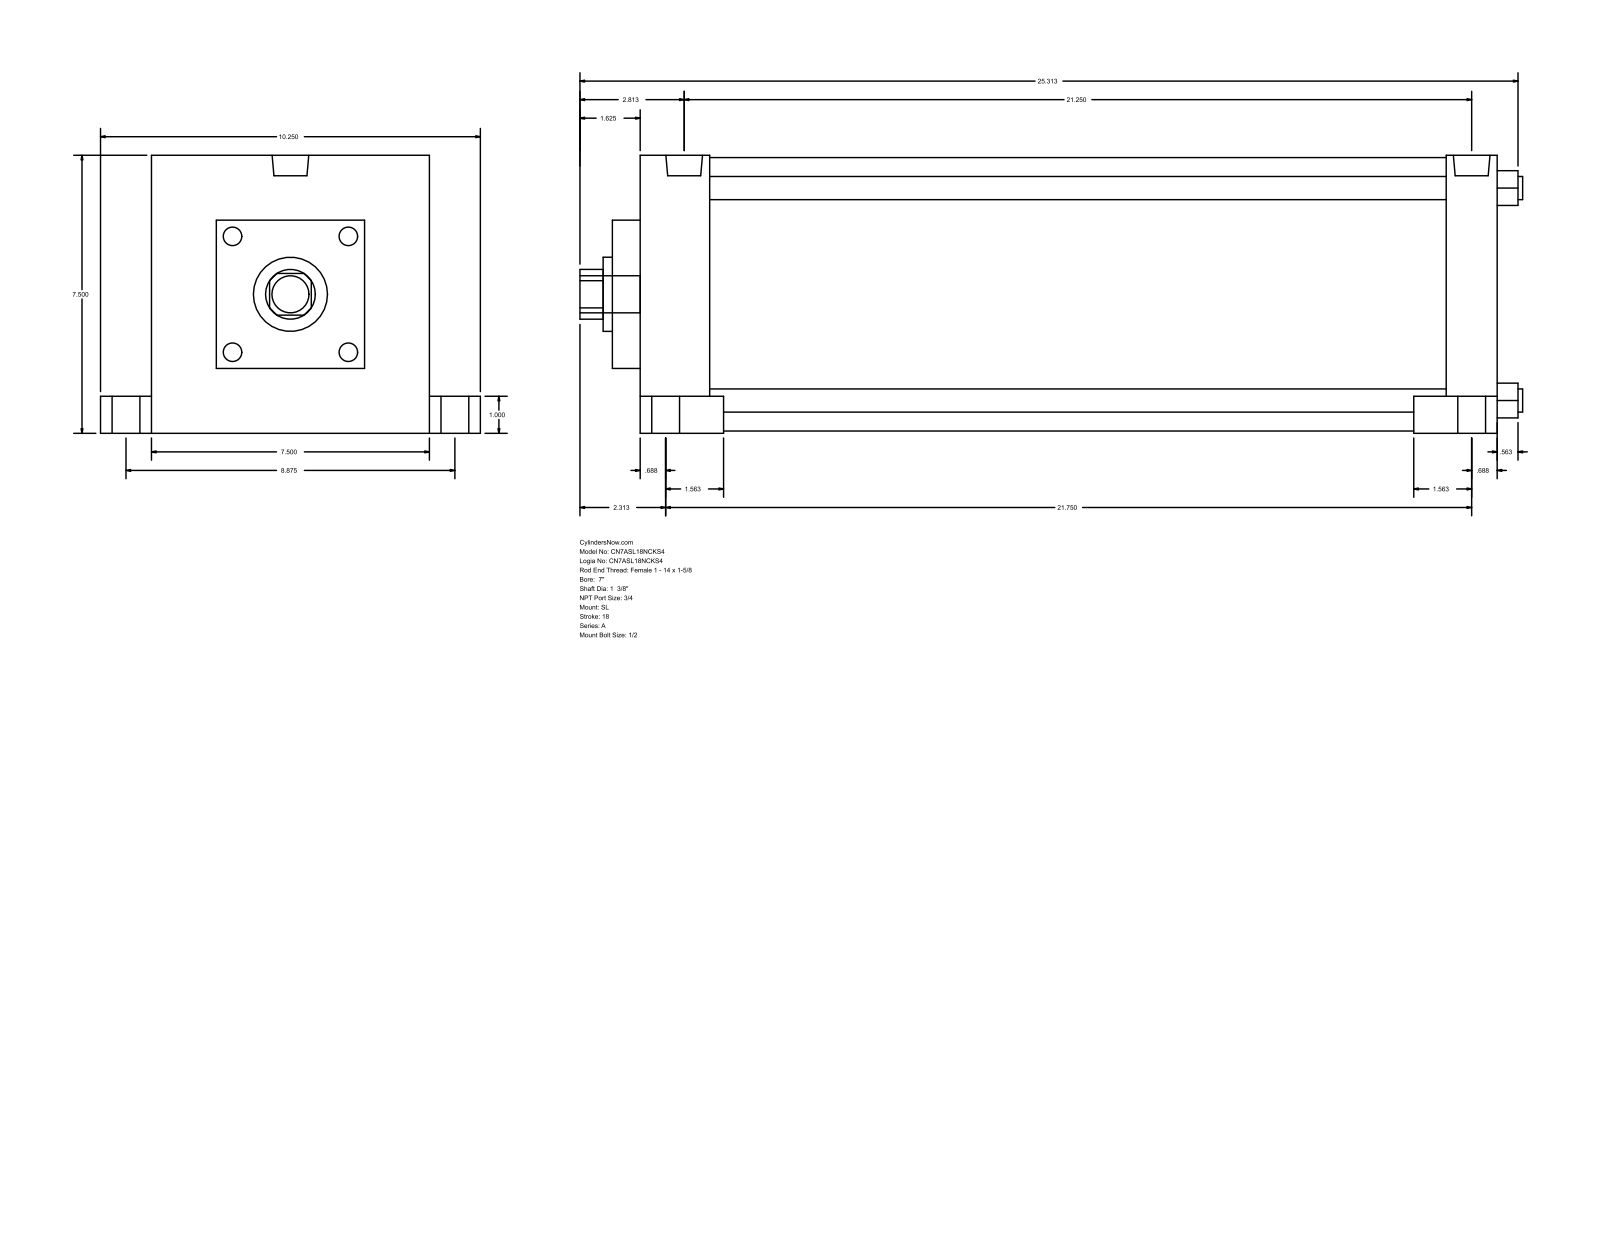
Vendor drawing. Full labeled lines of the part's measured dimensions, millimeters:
Part name (STEP PRODUCT): A_SL__0700_1.375
STEP written by: GSSL Pune (CONFIG_CONTROL_DESIGN)
Units: millimetres
Bodies: 0 solids, 117 faces (85 planar, 32 cylindrical, 0 other)
Overall size (bounding box): 646.11 × 260.35 × 190.5
Round holes (diameter × count): ⌀15.88 ×4, ⌀34.92 ×1, ⌀50.8 ×1, ⌀187.32 ×1
Round bosses / shafts (diameter × count): ⌀25.4 ×5, ⌀19.05 ×4, ⌀15.08 ×4, ⌀25.12 ×2
Partial cylindrical surfaces — rounded edges, fillets, slot ends (radius × count): R17.06 ×1
Main face-to-face distances: 190.5, 587.38, 19.04, 606.42, 571.5, 66.67, 47.63, 539.75, 552.46, 504.83
Hole centre spacings: 102.91, 145.54, 205.82
